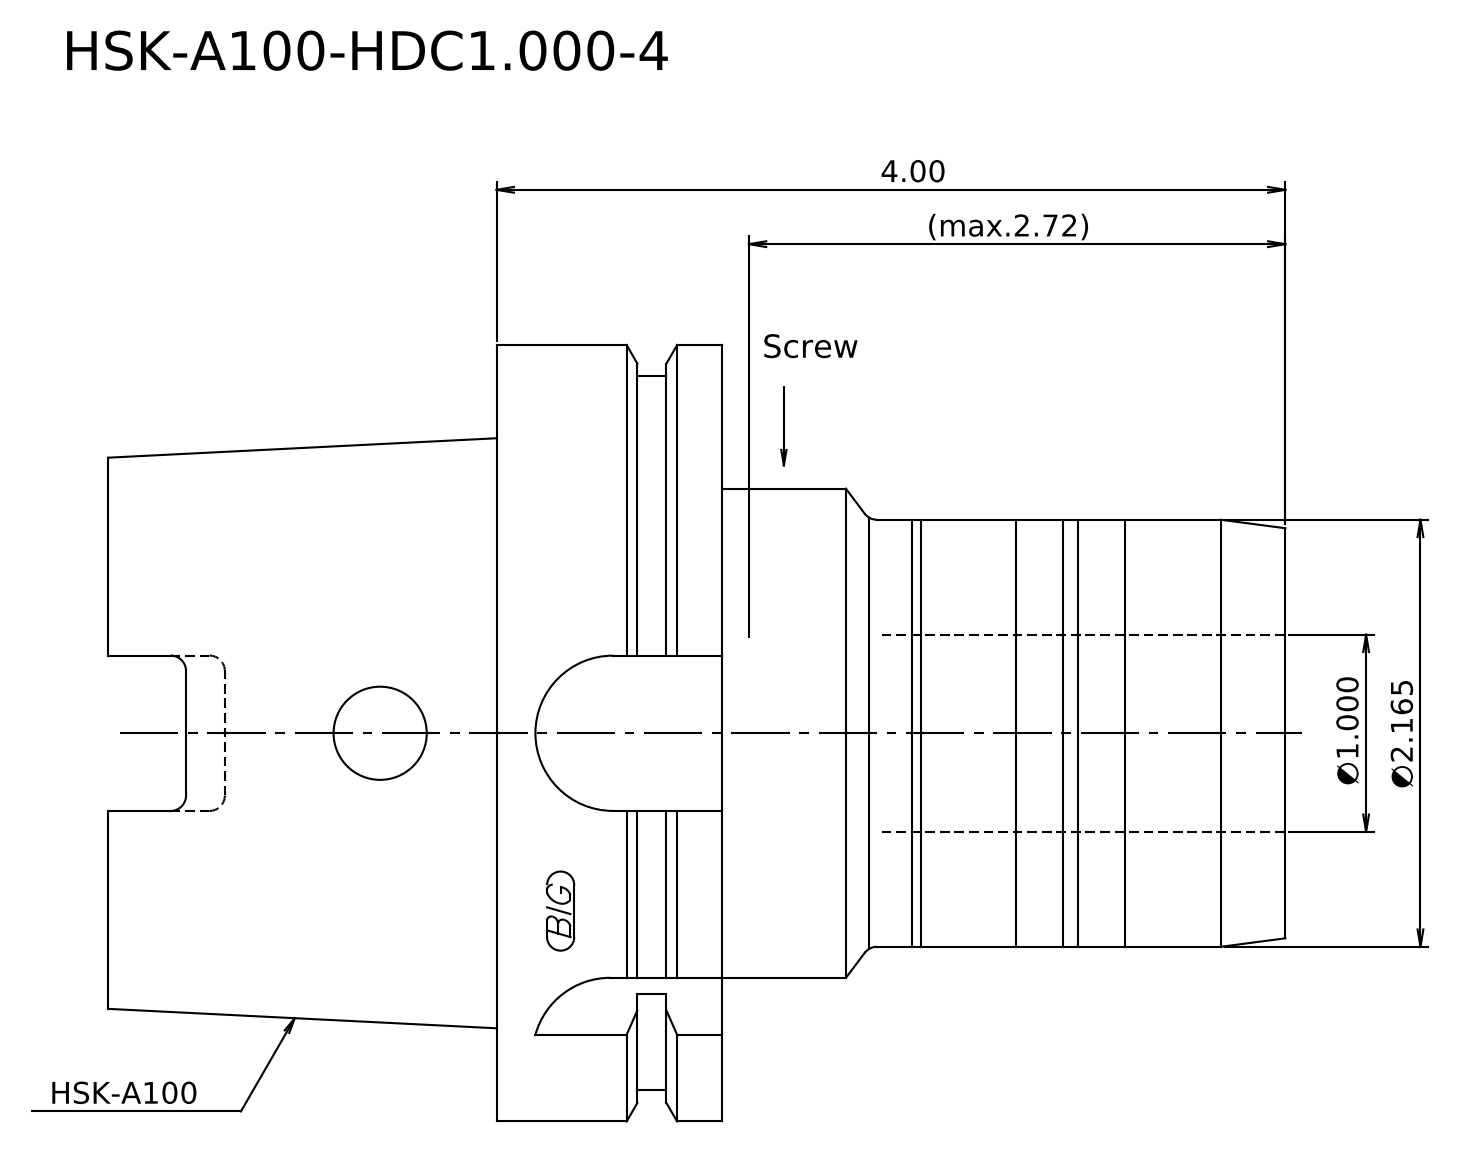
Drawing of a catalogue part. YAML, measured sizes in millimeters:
step_written_by: "Kubotek KeyCreator 2011 V10.0.2 (22737) (automotive_design)"
units: millimeters
bodies: {solids: 1, faces: 16, planar: 6, cylindrical: 5, other: 5}
overall_size: [151.6, 100, 100]
volume: 619486
surface_area: 49844
round_bosses_or_shafts:
  - {diameter: 100, count: 1}
  - {diameter: 92, count: 1}
  - {diameter: 63, count: 1}
  - {diameter: 55, count: 1}
face_to_face_distances: [79, 29, 50, 72.6, 101.6, 151.6, 79.72, 7.12, 21.88, 71.88]
